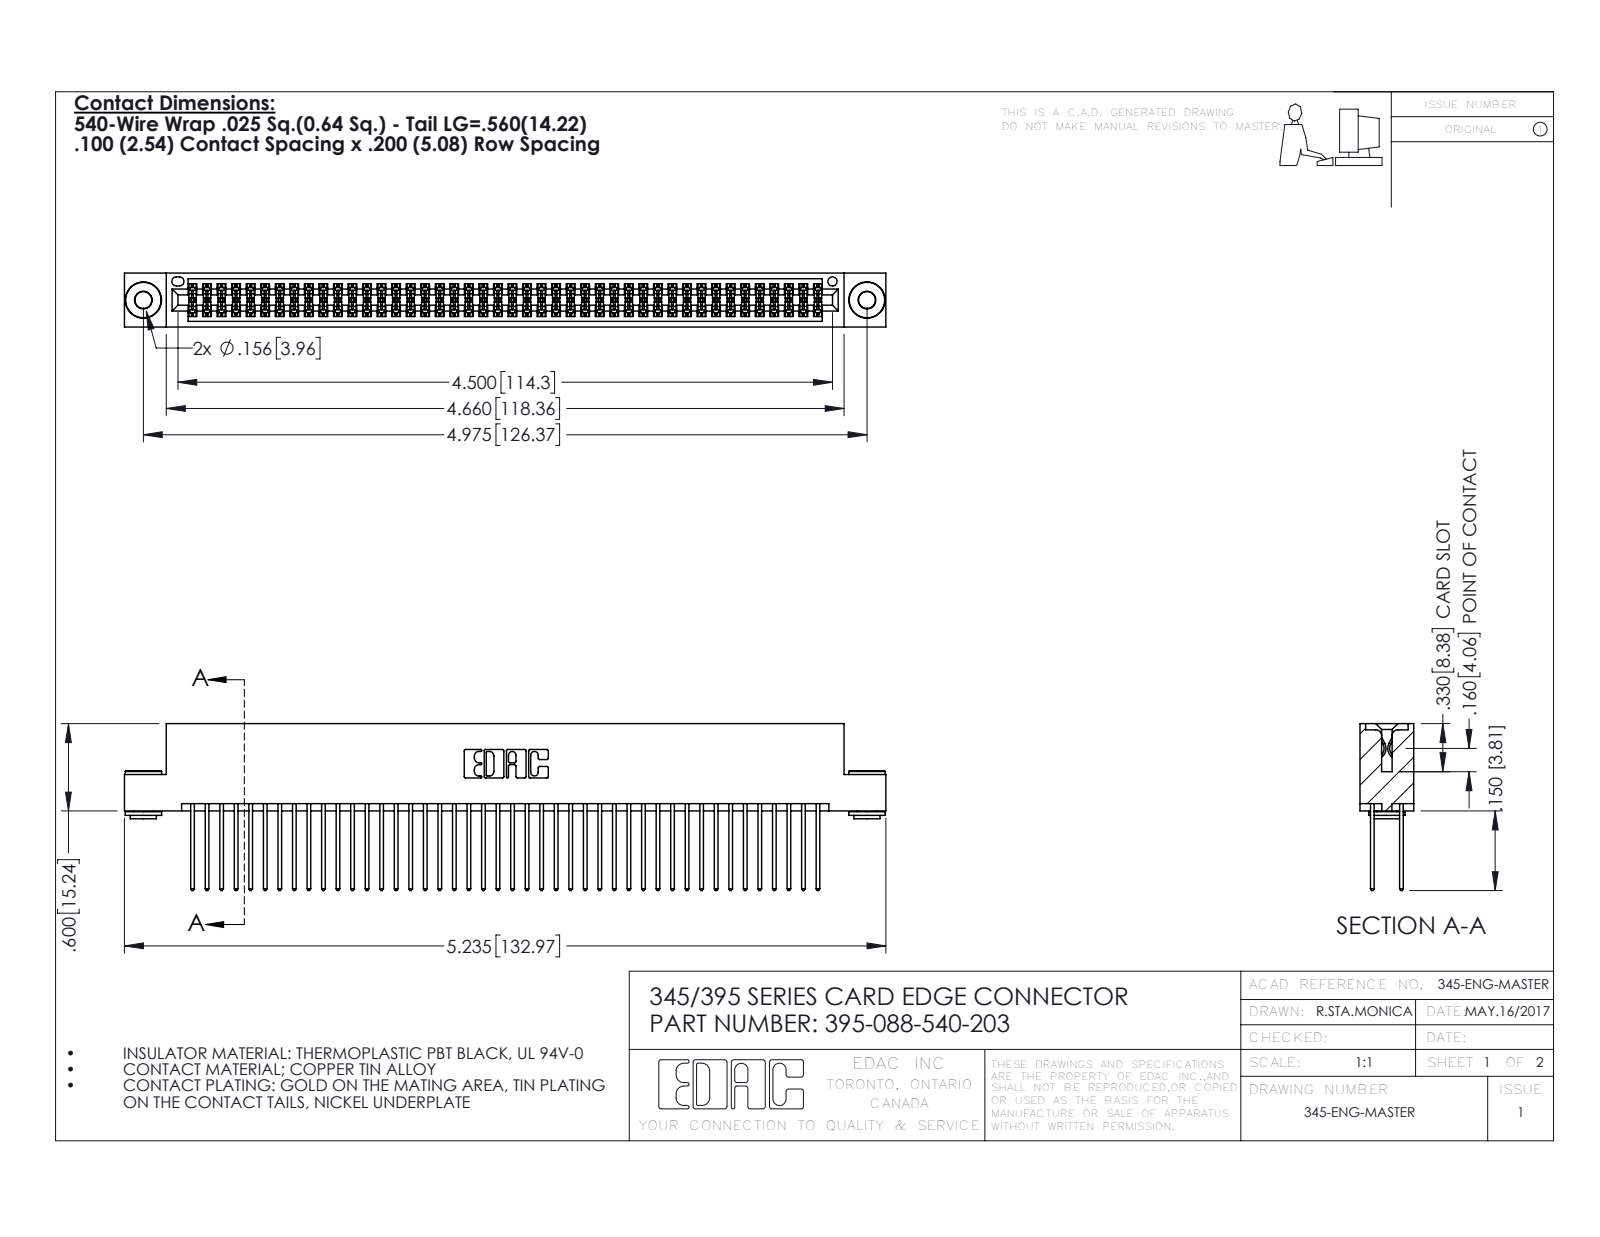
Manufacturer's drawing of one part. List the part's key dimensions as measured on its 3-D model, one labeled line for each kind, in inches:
Part name (STEP PRODUCT): 345 Part_Flush Mounting Lugs - 0.156 Dia-TH; 345-250-002_345-250-002-102; 395-088-540-203; 345-292-001_345-293-140
STEP written by: SolidWorks 2016 (CONFIG_CONTROL_DESIGN)
Units: inches
Bodies: 91 solids, 4564 faces (2994 planar, 1562 cylindrical, 8 other)
Overall size (bounding box): 5.235 × 1.147 × 0.37
Volume: 0.811 in³ · Surface area: 33.22 in²
Round holes (diameter × count): ⌀0.116 ×2, ⌀0.156 ×2, ⌀0.064 ×1
Round bosses / shafts (diameter × count): ⌀0.25 ×2, ⌀0.18 ×2, ⌀0.136 ×2
Partial cylindrical surfaces — rounded edges, fillets, slot ends (radius × count): R0.006 ×132, R0.01 ×88, R0.01 ×22, R0.007 ×6, R0.031 ×6, R0.026 ×3, R0.014 ×2, R0.019 ×2
Main face-to-face distances: 0.072, 0.298, 0.2, 0.025, 0.098, 0.272, 0.37, 0.225, 0.175, 0.149
Hole centre spacings: 0.27, 4.739, 4.975
